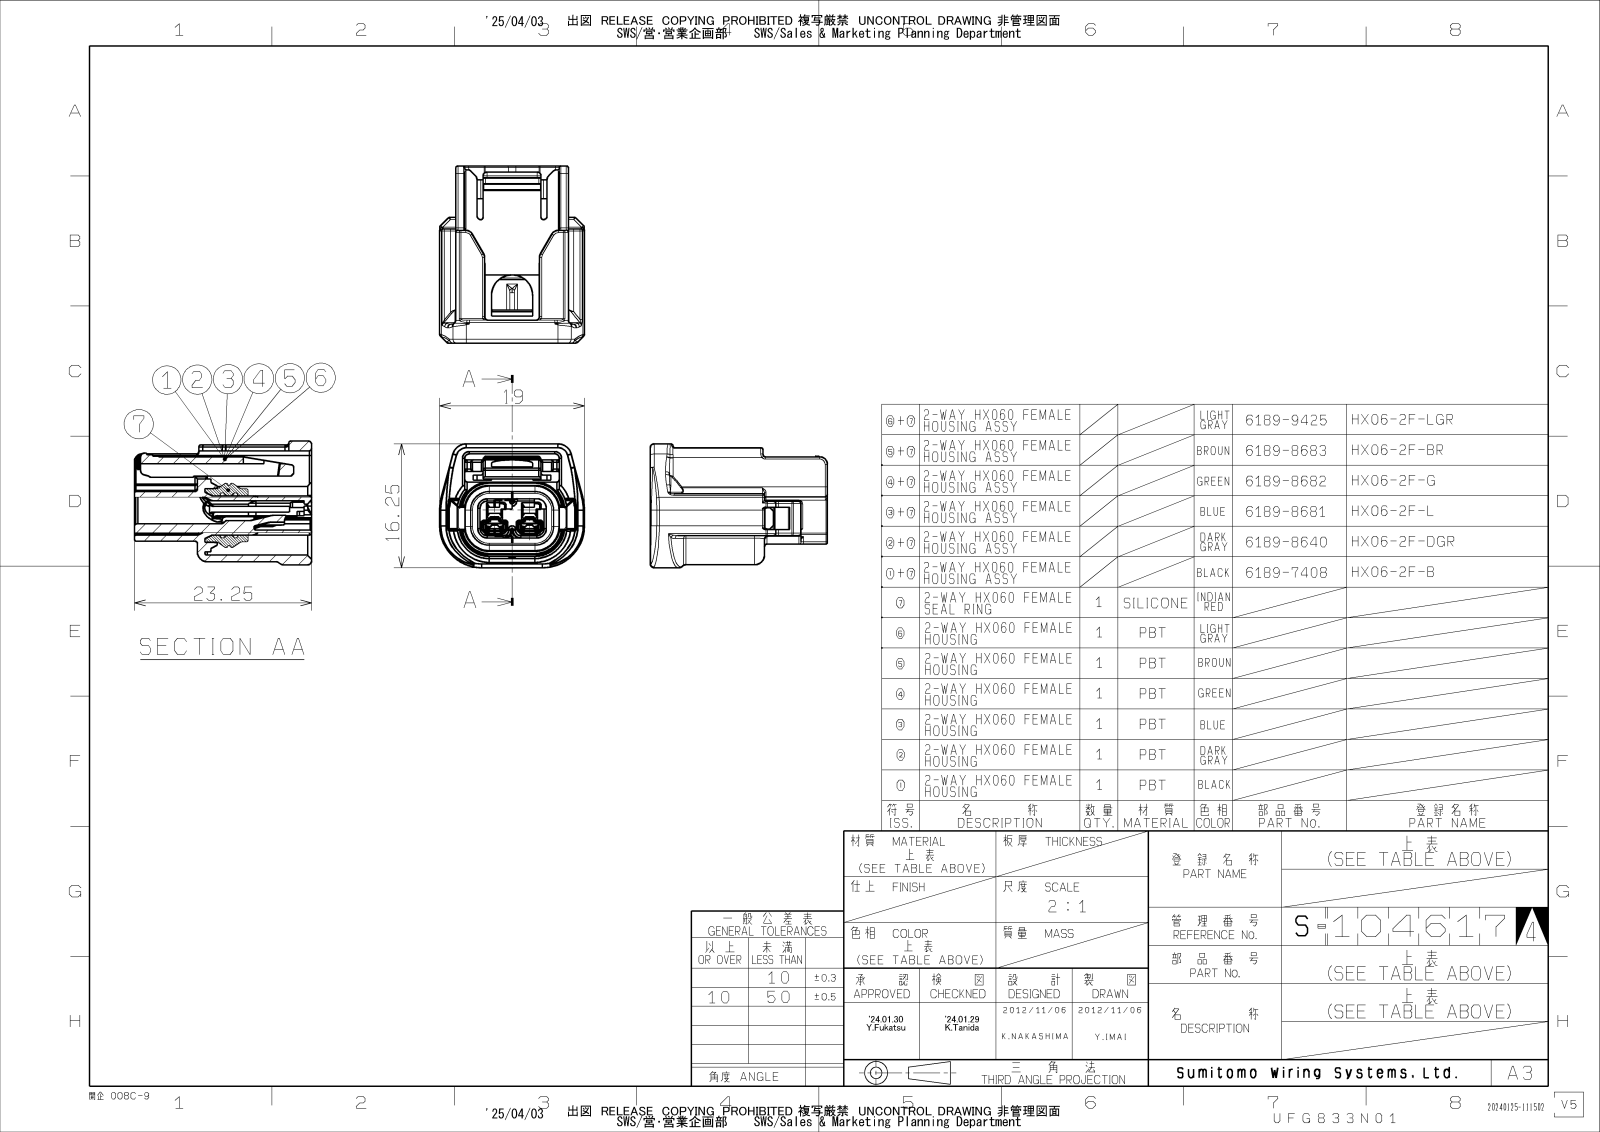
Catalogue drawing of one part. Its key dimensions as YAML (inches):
part_name: "6189-7408"
step_written_by: "CATIA V5 STEP AP214 v2 (AUTOMOTIVE_DESIGN)"
units: inches
bodies: {solids: 1, faces: 228, planar: 163, cylindrical: 52, other: 13}
overall_size: [0.915, 0.748, 0.64]
volume: 0.16
surface_area: 5.512
round_holes:
  - {diameter: 0.161, count: 2}
partial_cylinders:
  - {radius: 0.039, count: 7}
  - {radius: 0.049, count: 4}
  - {radius: 0.059, count: 4}
  - {radius: 0.071, count: 4}
  - {radius: 0.165, count: 4}
  - {radius: 0.051, count: 3}
  - {radius: 0.091, count: 2}
  - {radius: 0.116, count: 2}
face_to_face_distances: [0.031, 0.047, 0.535, 0.035, 0.083, 0.067, 0.142, 0.063, 0.541, 0.098]
hole_center_spacings: [0.181]
